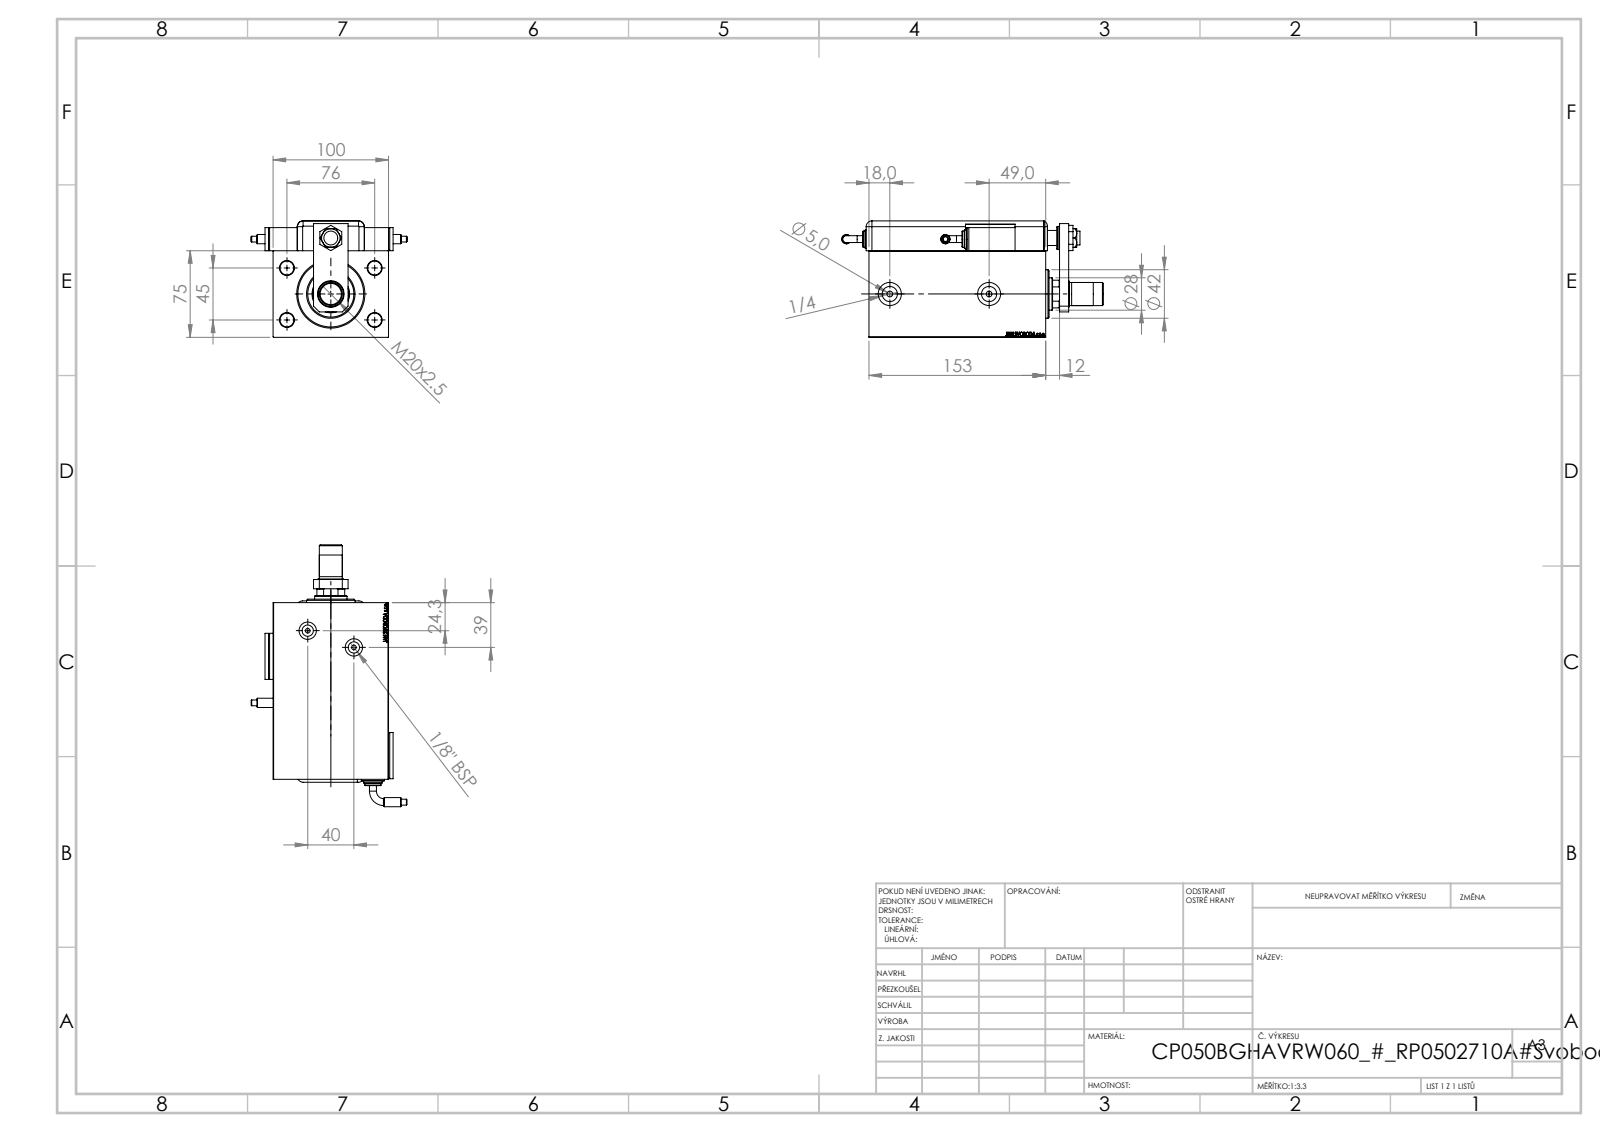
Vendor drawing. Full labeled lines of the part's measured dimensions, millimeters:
Part name (STEP PRODUCT): NUT_D19; SWITCH Q; SWITCH DIM A_G; NUT_D13 (+7 more)
STEP written by: SolidWorks 2019 (CONFIG_CONTROL_DESIGN)
Units: millimetres
Bodies: 15 solids, 1344 faces (624 planar, 139 cylindrical, 581 other)
Overall size (bounding box): 226.76 × 135.01 × 100.8
Volume: 1 231 000 mm³ · Surface area: 210 643 mm²
Round holes (diameter × count): ⌀12 ×5, ⌀4 ×4, ⌀5 ×2, ⌀8 ×2, ⌀9.73 ×2, ⌀13.16 ×2, ⌀15 ×2, ⌀20 ×2, ⌀13 ×1, ⌀14 ×1, ⌀18.5 ×1, ⌀28 ×1
Round bosses / shafts (diameter × count): ⌀20 ×4, ⌀16 ×2, ⌀14 ×2, ⌀8 ×2, ⌀6 ×2, ⌀5.04 ×2, ⌀42 ×1, ⌀18 ×1
Partial cylindrical surfaces — rounded edges, fillets, slot ends (radius × count): R5 ×9, R10 ×1, R13.5 ×1
Main face-to-face distances: 75, 3, 100, 25.8, 100.8, 20, 14, 97.8, 153, 22.8
Hole centre spacings: 44.16, 45, 46.04, 76, 80.53, 88.32, 18.28, 20
